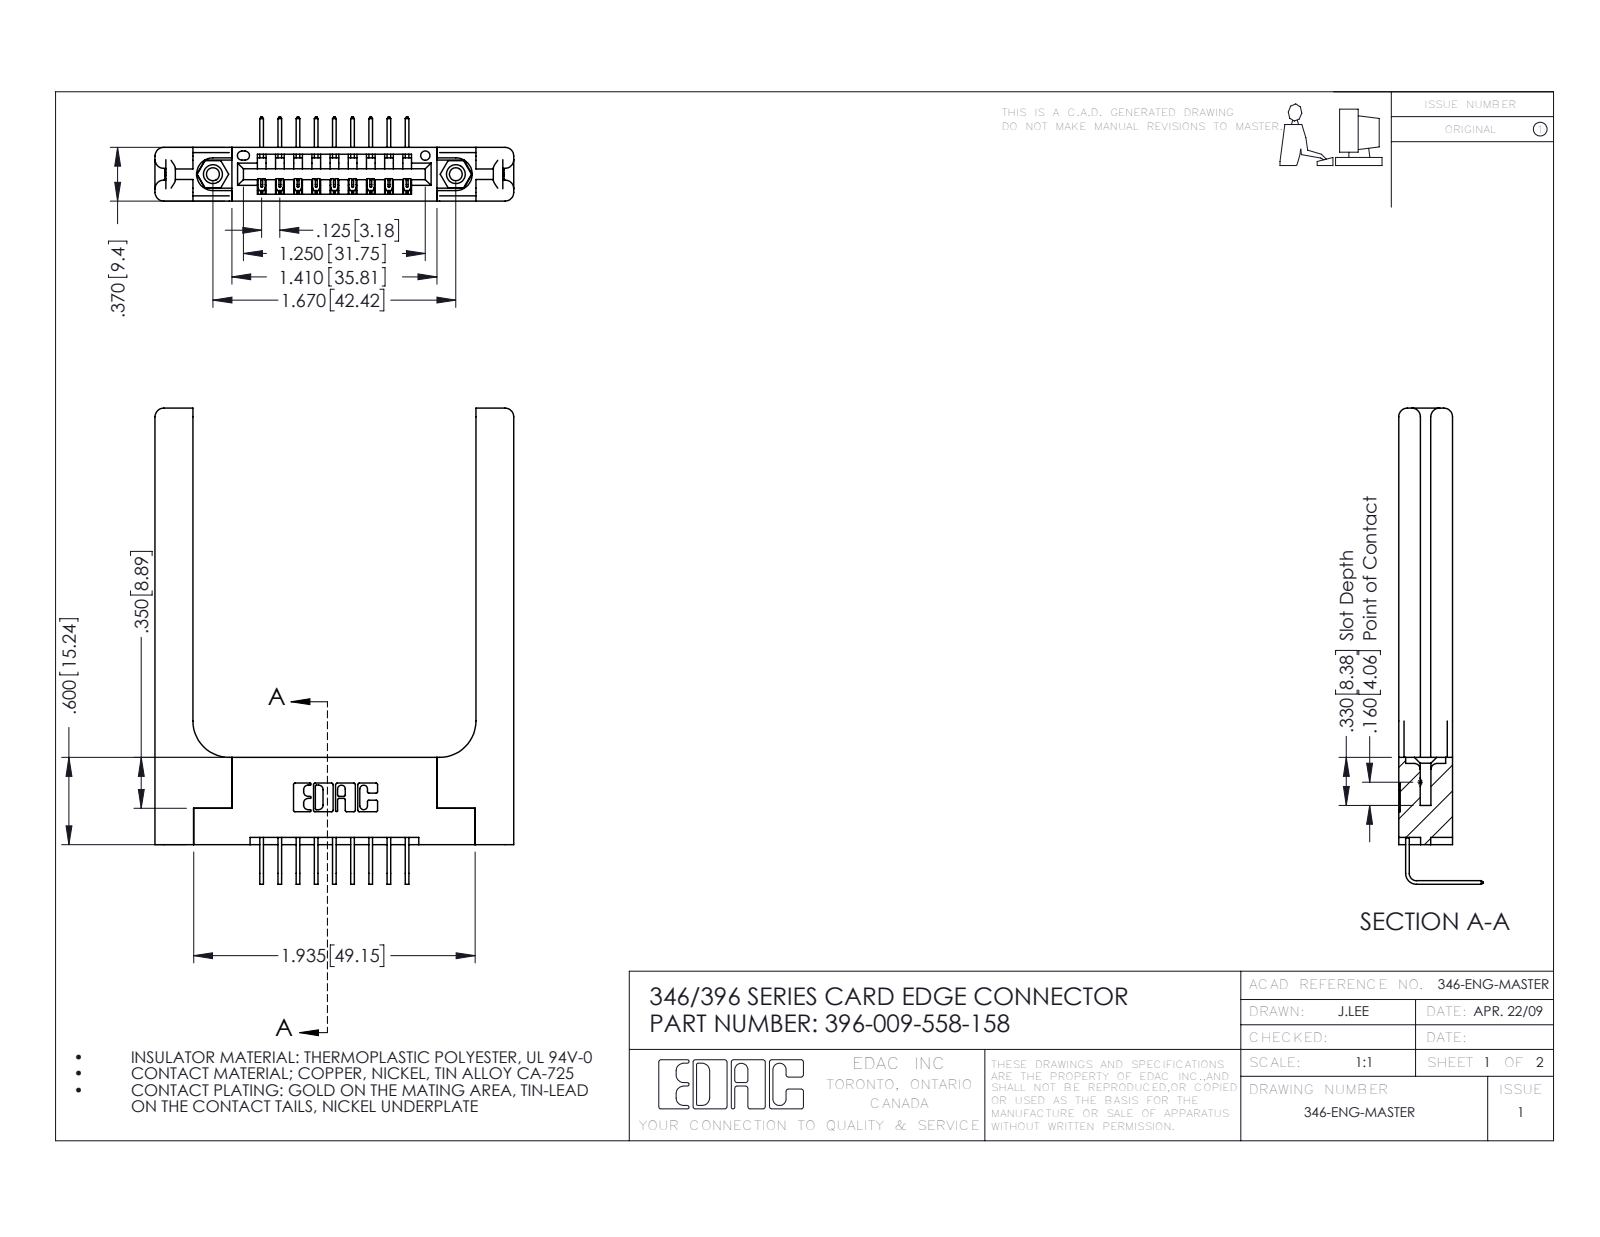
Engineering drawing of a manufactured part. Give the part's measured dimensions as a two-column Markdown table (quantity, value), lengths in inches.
| quantity | value |
| --- | --- |
| part name | 345-250-001_345-250-001-102; 346-220-058_345-220-058; 345-292-001_558 Tail - 2; 396-009-558-158 (+1 more) |
| STEP written by | SolidWorks 2016 (CONFIG_CONTROL_DESIGN) |
| units | inches |
| bodies | 14 solids, 918 faces (602 planar, 256 cylindrical, 60 other) |
| overall size | 3.273 × 2.466 × 0.58 |
| volume | 0.813 in³ |
| surface area | 18.97 in² |
| round holes (diameter × count) | 0.089 × 2, 0.125 × 2, 0.156 × 2, 0.064 × 1 |
| round bosses / shafts (diameter × count) | 0.155 × 2 |
| partial cylindrical surfaces (radius × count) | 0.01 × 22, 0.006 × 18, 0.06 × 16, 0.007 × 6, 0.031 × 6, 0.026 × 3, 0.03 × 2, 0.031 × 2 |
| main face-to-face distances | 0.37, 0.15, 0.22, 0.072, 0.148, 0.322, 0.25, 0.048, 0.102, 0.173 |
| hole center spacings | 0.246, 1.465, 1.67 |
